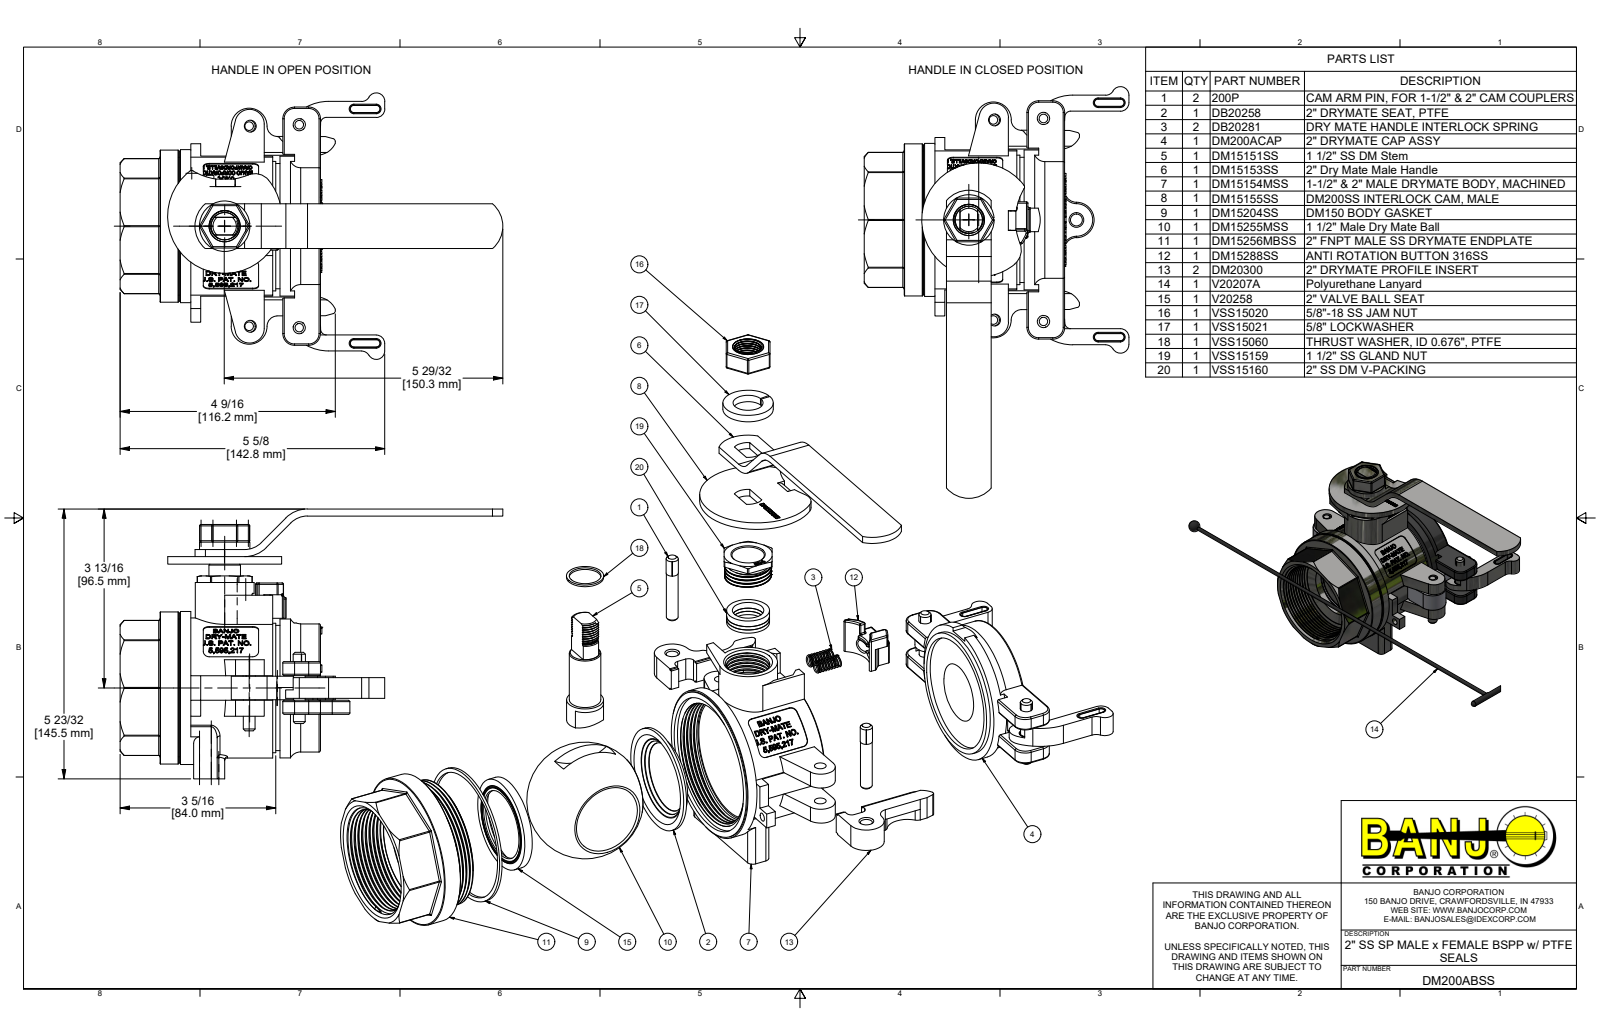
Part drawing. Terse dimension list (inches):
name: DM200ABSS; DM15154MSS; DB20258; DB20281 (+8 more)
written by: Autodesk Inventor 2022 (AUTOMOTIVE_DESIGN)
unit: in
bodies: 33 solids, 2804 faces (1190 planar, 571 cylindrical, 1043 other)
size: 11.984 × 7.594 × 5.73
volume: 25.58 in³; area: 295.7 in²
holes: 5× ⌀0.25, 4× ⌀0.256, 3× ⌀0.125, 2× ⌀1.5, 1× ⌀0.18, 1× ⌀0.64, 1× ⌀0.662, 1× ⌀0.67, 1× ⌀0.676, 1× ⌀0.69, 1× ⌀0.84, 1× ⌀0.876
bosses: 4× ⌀0.26, 4× ⌀0.249, 3× ⌀0.28, 1× ⌀3.23, 1× ⌀3.19, 1× ⌀2.975, 1× ⌀2.97, 1× ⌀2.945
rounds: 98× R0.03, 8× R0.06, 8× R0.125, 6× R0.18, 6× R0.25, 4× R0.025, 4× R0.075, 4× R0.12
face distances: 0.86, 0.31, 0.298, 0.15, 1.17, 0.85, 0.822, 0.16, 1.02, 1.01
hole spacings: 4.25, 0.95, 1.646, 0.025, 1.041, 1.065, 2.187, 2.194
